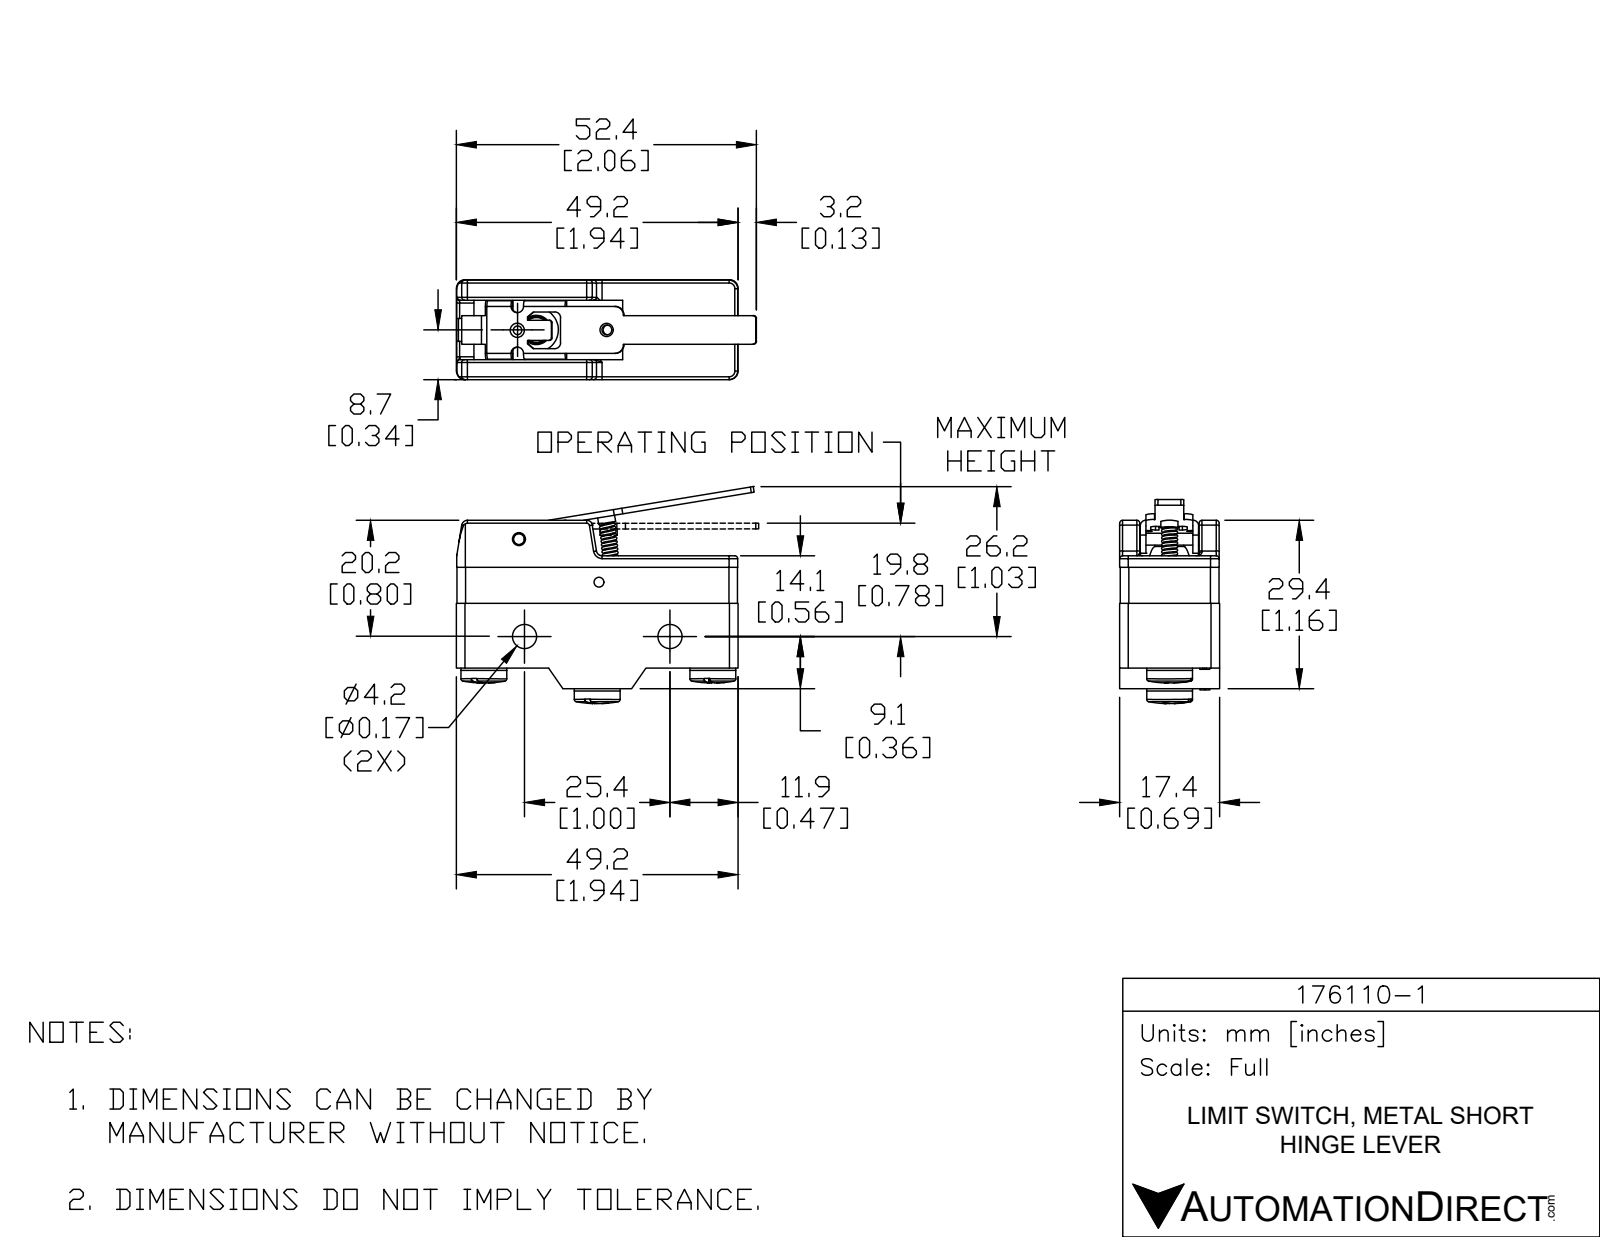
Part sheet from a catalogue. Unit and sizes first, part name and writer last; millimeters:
Units: millimetres
Overall size (bounding box): 52.4 × 35.6 × 17.4
Round holes (diameter × count): ⌀3.8 ×3, ⌀6 ×3, ⌀1.7 ×2, ⌀4.2 ×2, ⌀2 ×1, ⌀4.6 ×1, ⌀5 ×1
Round bosses / shafts (diameter × count): ⌀8 ×3, ⌀5.5 ×1, ⌀3 ×1, ⌀2.1 ×1
Partial cylindrical surfaces — rounded edges, fillets, slot ends (radius × count): R0.5 ×21, R1.5 ×14, R0.3 ×12, R1 ×7, R2.9 ×3, R0.4 ×2, R0.8 ×2, R1.1 ×2
Main face-to-face distances: 1, 17.3, 17.6, 17.4, 2, 19.6, 3.5, 3.6, 13.9, 17.3
Hole centre spacings: 1.9, 9.2, 10.6, 12.5, 15.6, 15.8, 16.1, 17
Volume: 17 700 mm³ · Surface area: 10 120 mm²
Bodies: 11 solids, 591 faces (250 planar, 151 cylindrical, 190 other)
Part name (STEP PRODUCT): 176-MS (Screw Terminal)-Short Hinge Lever
STEP written by: SolidWorks 2018 (AUTOMOTIVE_DESIGN)
